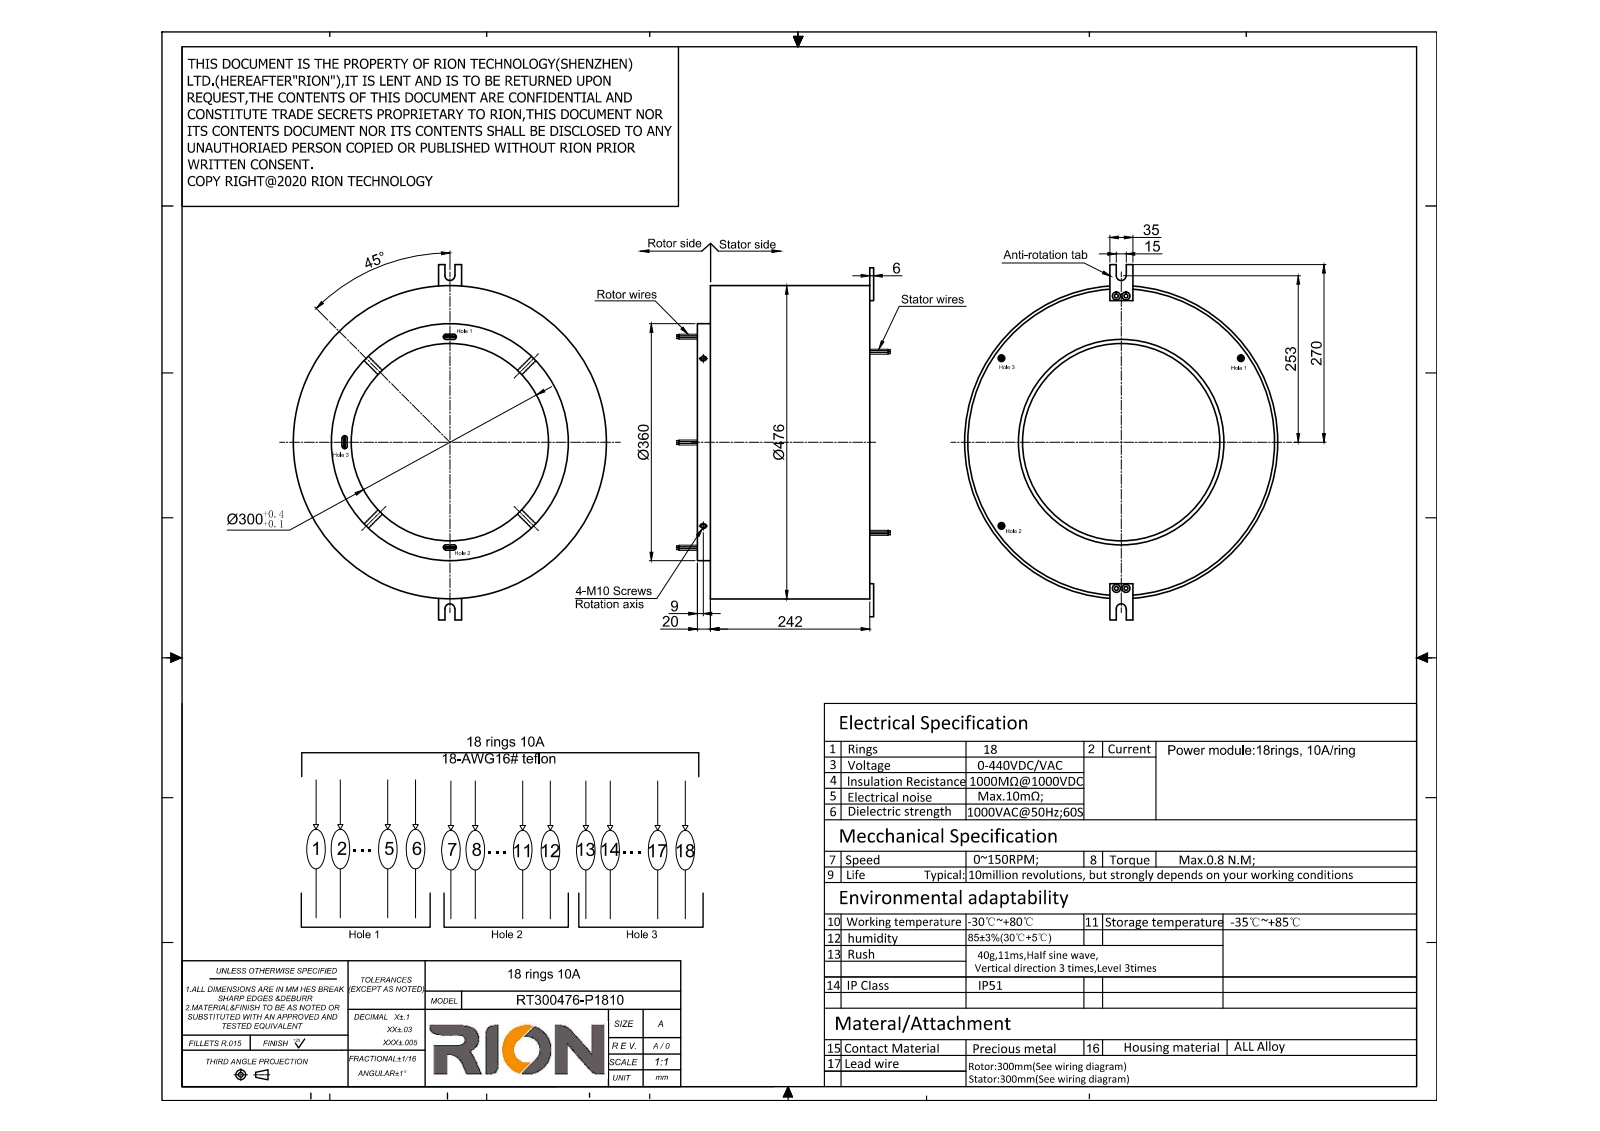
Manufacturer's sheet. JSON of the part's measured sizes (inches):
{"part_name": "RT300476-P1810", "step_written_by": "SolidWorks 2014 (CONFIG_CONTROL_DESIGN)", "units": "inches", "bodies": {"solids": 1, "faces": 218, "planar": 72, "cylindrical": 130, "other": 16}, "overall_size": [21.26, 18.74, 17.283], "volume_in3": 1623, "surface_area_in2": 1420, "round_holes": [[0.197, 4], [0.335, 4], [0.394, 3], [11.811, 1], [12.291, 1], [18.346, 1]], "round_bosses_or_shafts": [[0.083, 36], [18.74, 1], [18.339, 1], [14.173, 1], [12.283, 1]], "partial_cylinders_radius": [[0.157, 6], [0.295, 2], [6.457, 1]], "face_to_face_distances": [9.528, 0.787, 10.315, 10.551, 9.764, 0.236, 1.378, 0.984, 0.394, 0.197], "hole_center_spacings": [8.746, 7.776, 8.37, 8.74, 15.354, 15.662, 0.669, 17.48]}
